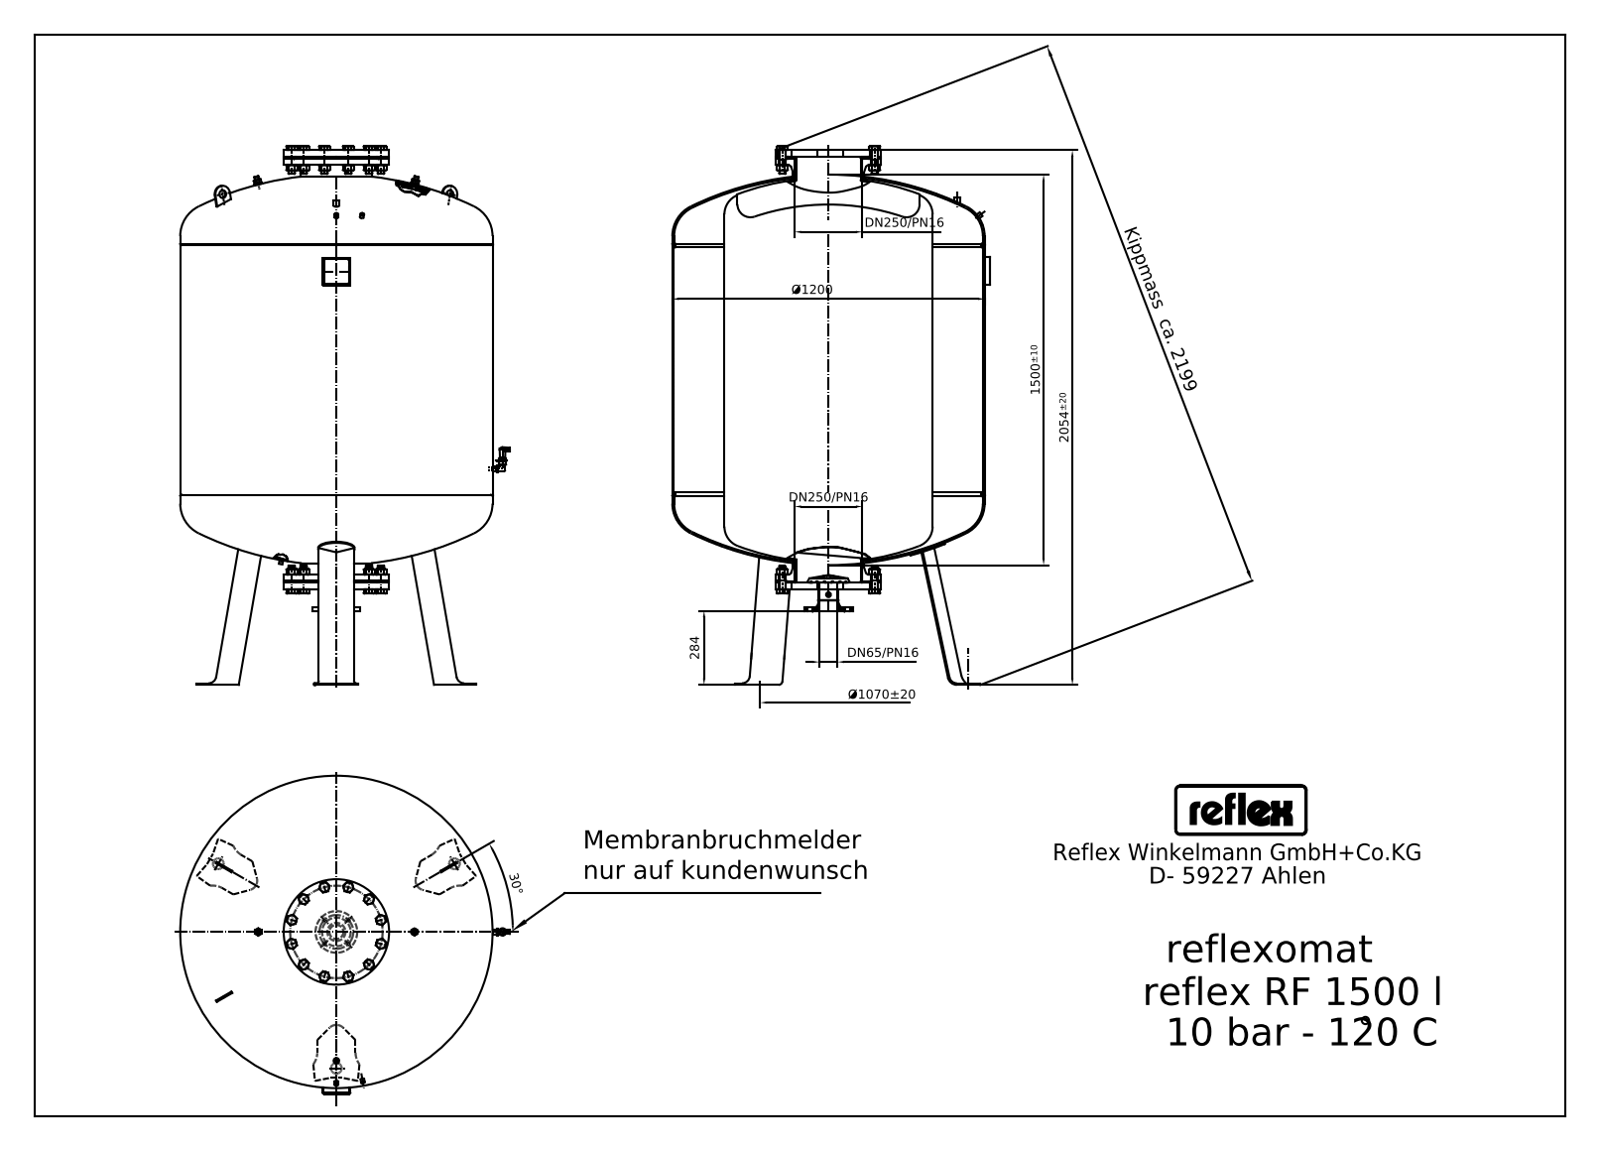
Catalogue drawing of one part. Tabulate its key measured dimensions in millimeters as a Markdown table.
| quantity | value |
| --- | --- |
| STEP written by | Mechanical Desktop 2009 (CONFIG_CONTROL_DESIGN) |
| units | millimeters |
| bodies | 23 solids, 940 faces (556 planar, 222 cylindrical, 162 other) |
| overall size | 2060 × 1266 × 1220 |
| volume | 1 536 000 000 mm³ |
| surface area | 13 380 000 mm² |
| round holes (diameter × count) | 11.45 × 2, 3.5 × 1, 14.95 × 1, 30 × 1, 260.4 × 1 |
| round bosses / shafts (diameter × count) | 16 × 12, 21.3 × 3, 18.5 × 3, 28 × 2, 20 × 2, 1200 × 1, 375 × 1, 273 × 1 |
| partial cylindrical surfaces (radius × count) | 25 × 18, 1 × 5, 8.44 × 4, 3.38 × 3, 6 × 3, 9 × 3, 2 × 2, 3 × 2 |
| main face-to-face distances | 1000, 22, 1666, 27, 1639, 1313, 313, 1335, 335, 353 |
| hole center spacings | 495, 619.5, 792.97 |
